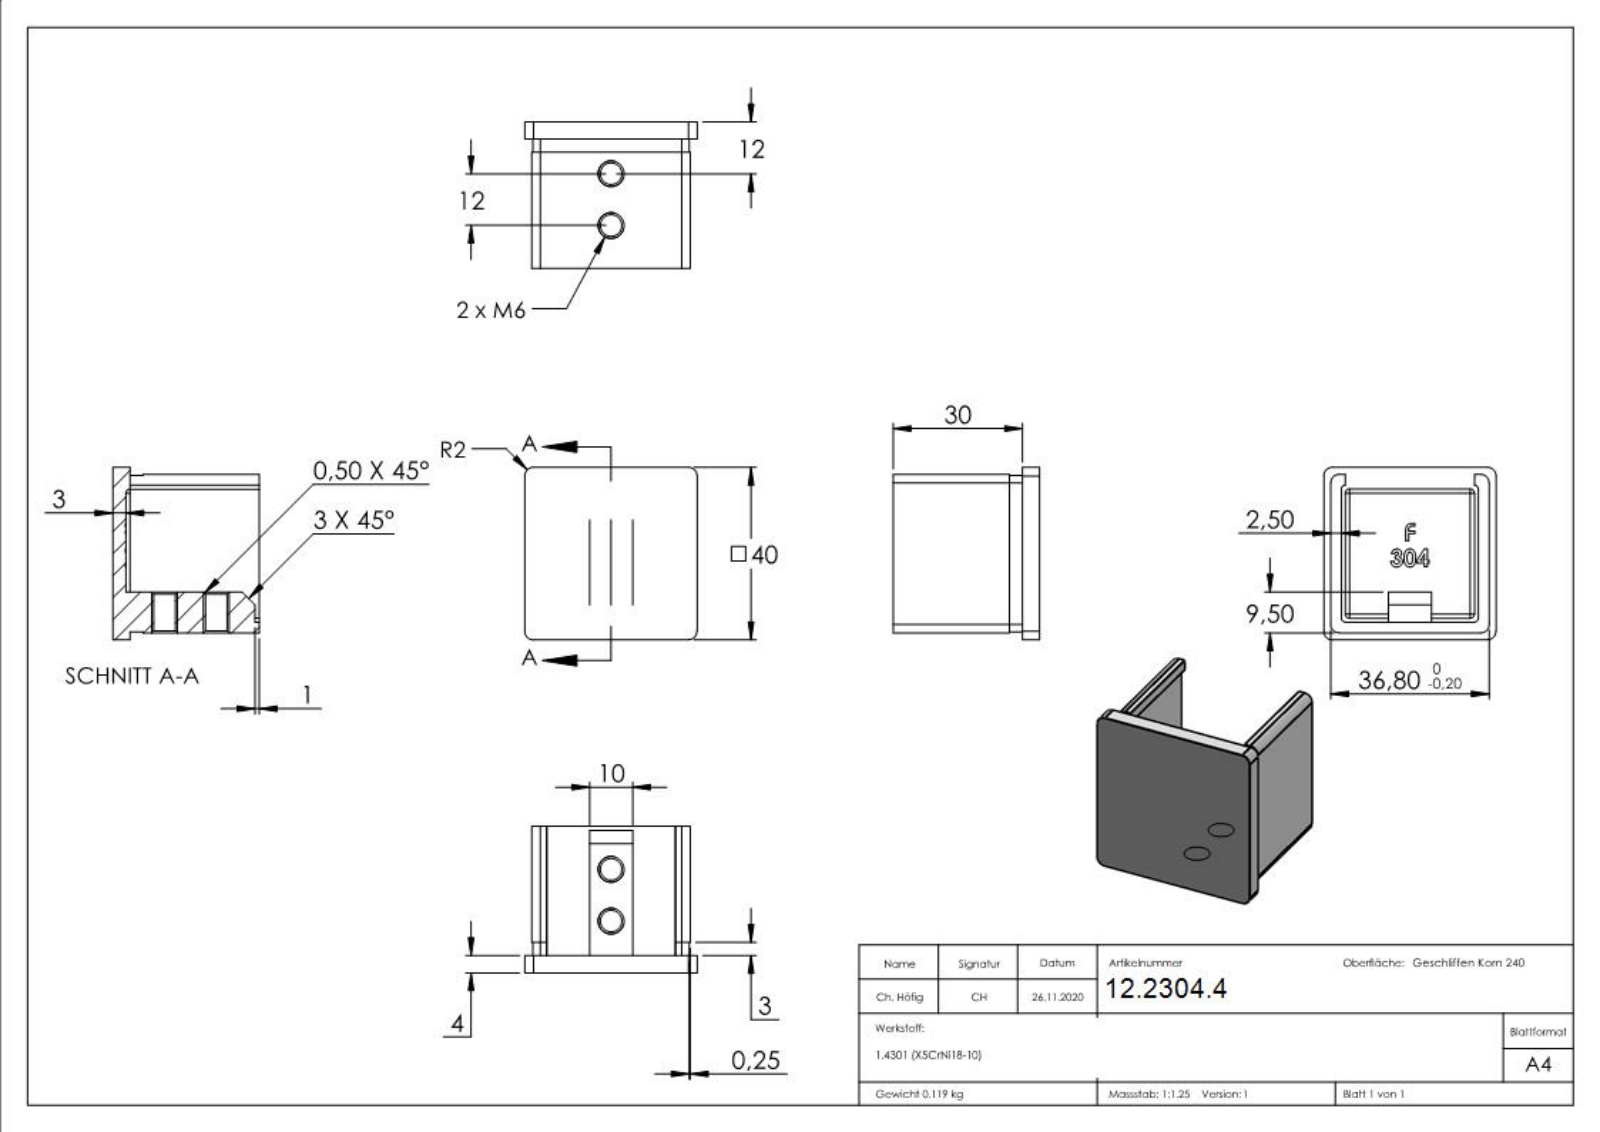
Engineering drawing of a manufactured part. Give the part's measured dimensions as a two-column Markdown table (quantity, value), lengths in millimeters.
| quantity | value |
| --- | --- |
| part name | 60319-240 |
| STEP written by | SolidWorks 2018 (CONFIG_CONTROL_DESIGN) |
| units | millimeters |
| bodies | 1 solid, 353 faces (187 planar, 25 cylindrical, 141 other) |
| overall size | 40 × 40 × 34 |
| volume | 15 050 mm³ |
| surface area | 10 979 mm² |
| round holes (diameter × count) | 5 × 2 |
| partial cylindrical surfaces (radius × count) | 1 × 8, 2 × 8, 1.75 × 4 |
| main face-to-face distances | 2.5, 34.3, 36.8, 31.8, 3, 1.6, 38.4, 1, 4, 4.1 |
| hole center spacings | 12 |
